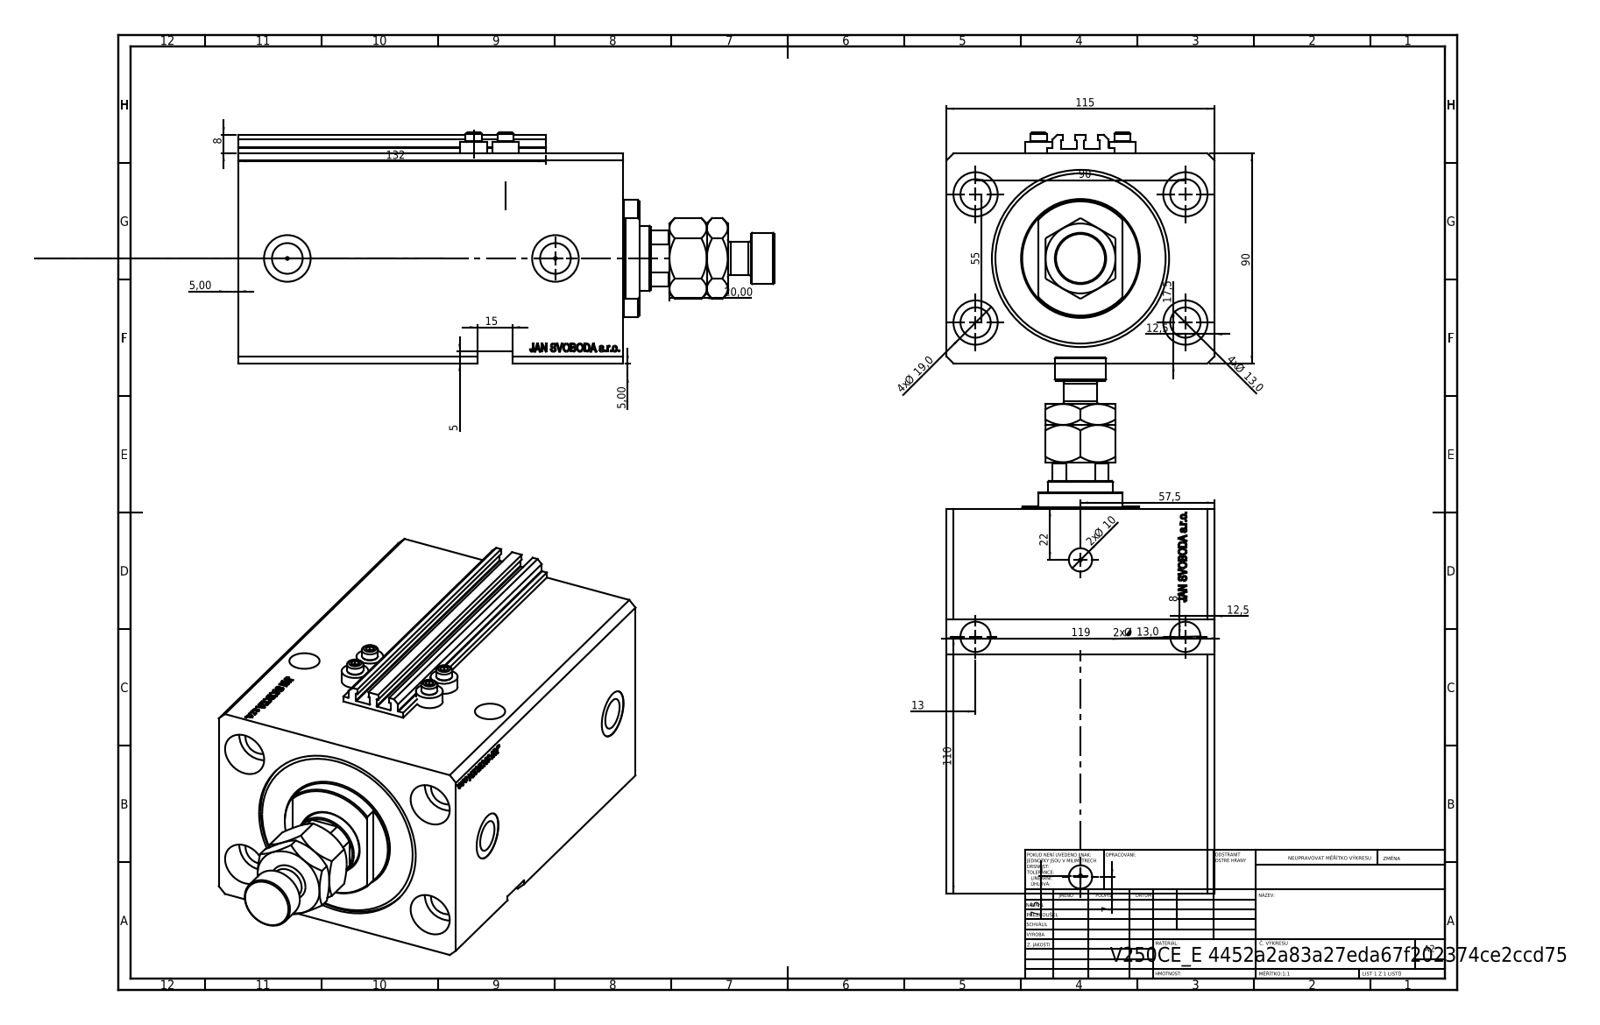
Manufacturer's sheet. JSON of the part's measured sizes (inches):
{"part_name": "MFA; ALLEN BOLT V250CE; V250CE_C_VCP; V250CE_VC_E (+1 more)", "step_written_by": "SolidWorks 2019 (CONFIG_CONTROL_DESIGN)", "units": "inches", "bodies": {"solids": 9, "faces": 1175, "planar": 563, "cylindrical": 142, "other": 470}, "overall_size": [9.051, 4.528, 3.898], "volume_in3": 86.71, "surface_area_in2": 341.7, "round_holes": [[0.512, 6], [0.049, 4], [0.157, 4], [0.748, 4], [0.394, 2], [0.518, 2], [0.787, 2], [0.728, 1], [1.102, 1], [2.48, 1], [2.992, 1]], "round_bosses_or_shafts": [[0.457, 4], [0.276, 4], [1.969, 1], [0.866, 1], [0.551, 1]], "partial_cylinders_radius": [[0.008, 10], [0.531, 1]], "face_to_face_distances": [3.543, 4.528, 6.496, 0.705, 5.791, 4.606, 5.311, 1.185, 2.161, 3.15], "hole_center_spacings": [2.076, 3.543, 0.535, 1.078, 1.12, 1.324, 1.417, 1.515]}
